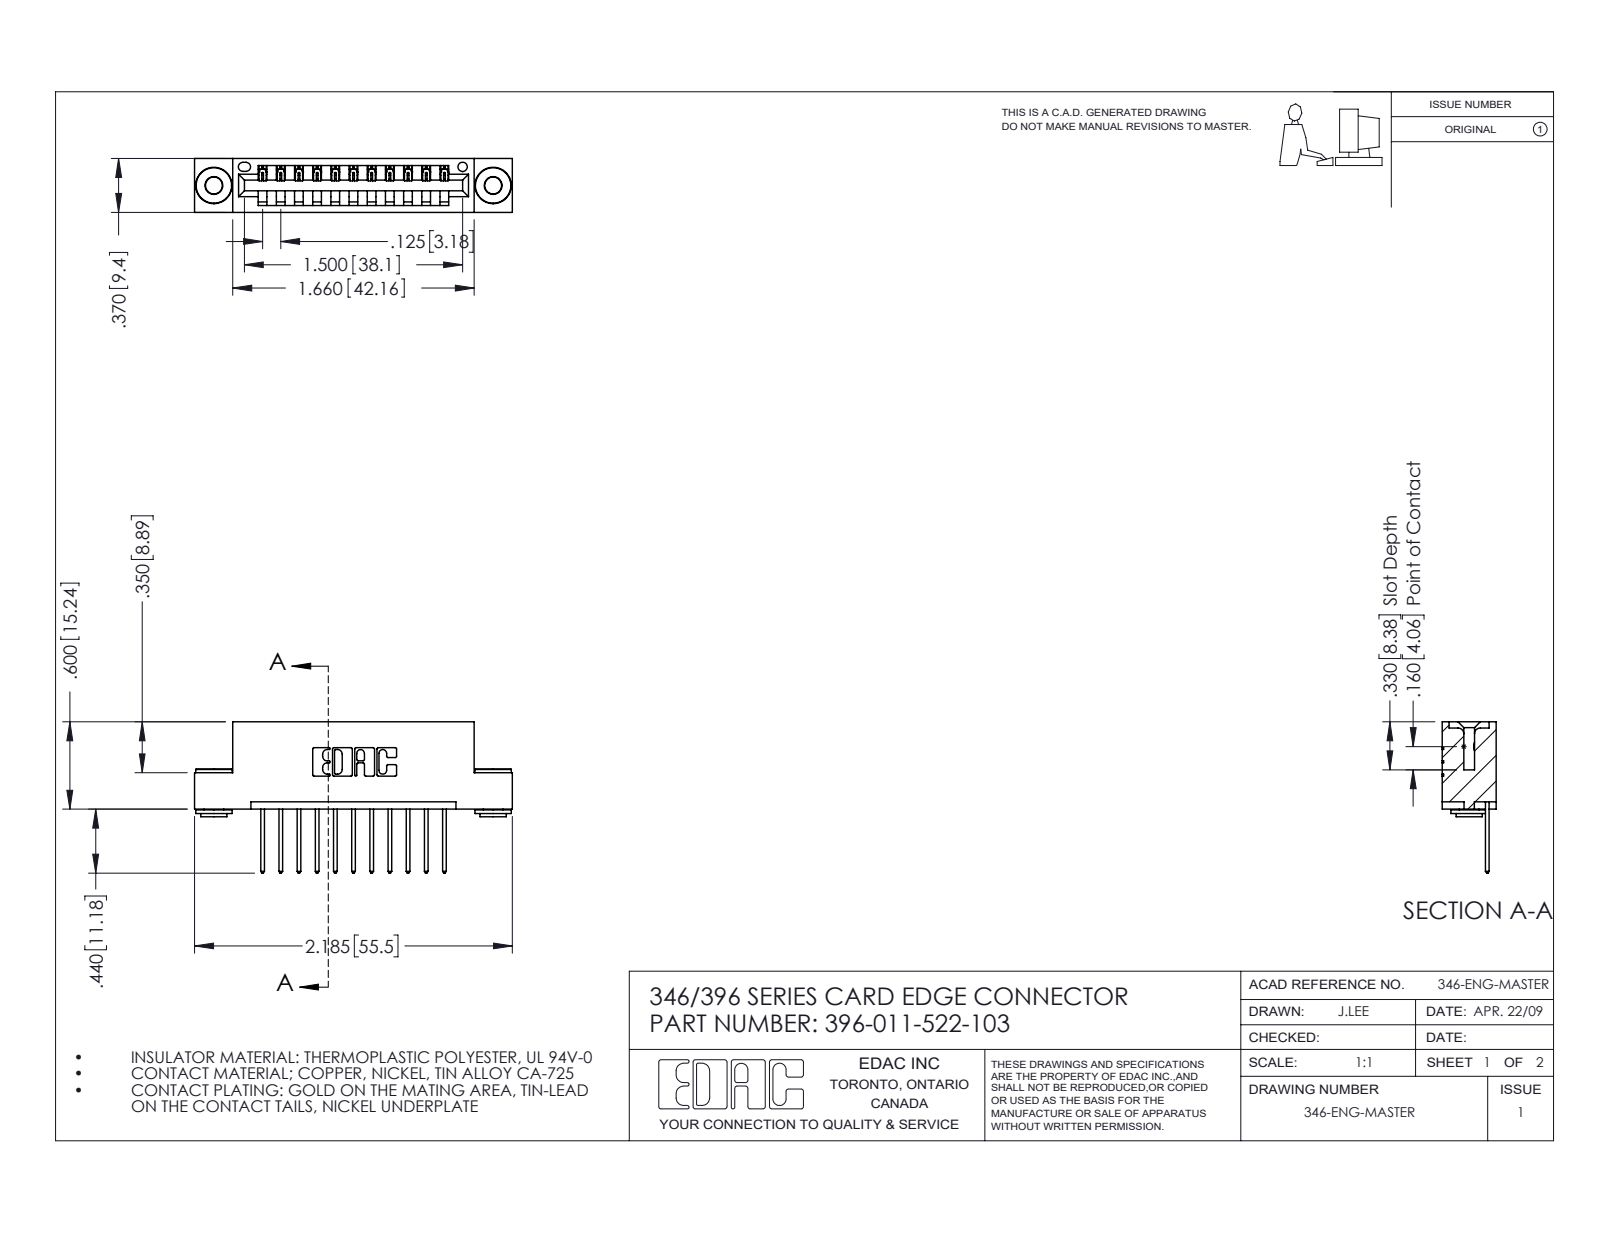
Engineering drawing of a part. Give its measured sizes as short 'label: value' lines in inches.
name: 345-292-001_345-293-122; 346 Part_Flush Mounting Lugs - 0.156 Dia-TH; 345-250-002_345-250-002-102; 396-011-522-103
written by: SolidWorks 2016 (CONFIG_CONTROL_DESIGN)
unit: in
bodies: 14 solids, 798 faces (526 planar, 264 cylindrical, 8 other)
size: 2.185 × 1.04 × 0.37
volume: 0.312 in³; area: 9.802 in²
holes: 2× ⌀0.116, 2× ⌀0.156, 1× ⌀0.064
bosses: 2× ⌀0.25, 2× ⌀0.18, 2× ⌀0.136
rounds: 22× R0.006, 22× R0.01, 22× R0.01, 6× R0.007, 6× R0.031, 3× R0.026, 2× R0.031, 2× R0.04
face distances: 0.25, 0.048, 0.322, 0.37, 0.025, 0.072, 0.298, 0.148, 0.222, 0.1
hole spacings: 0.246, 1.715, 1.92
